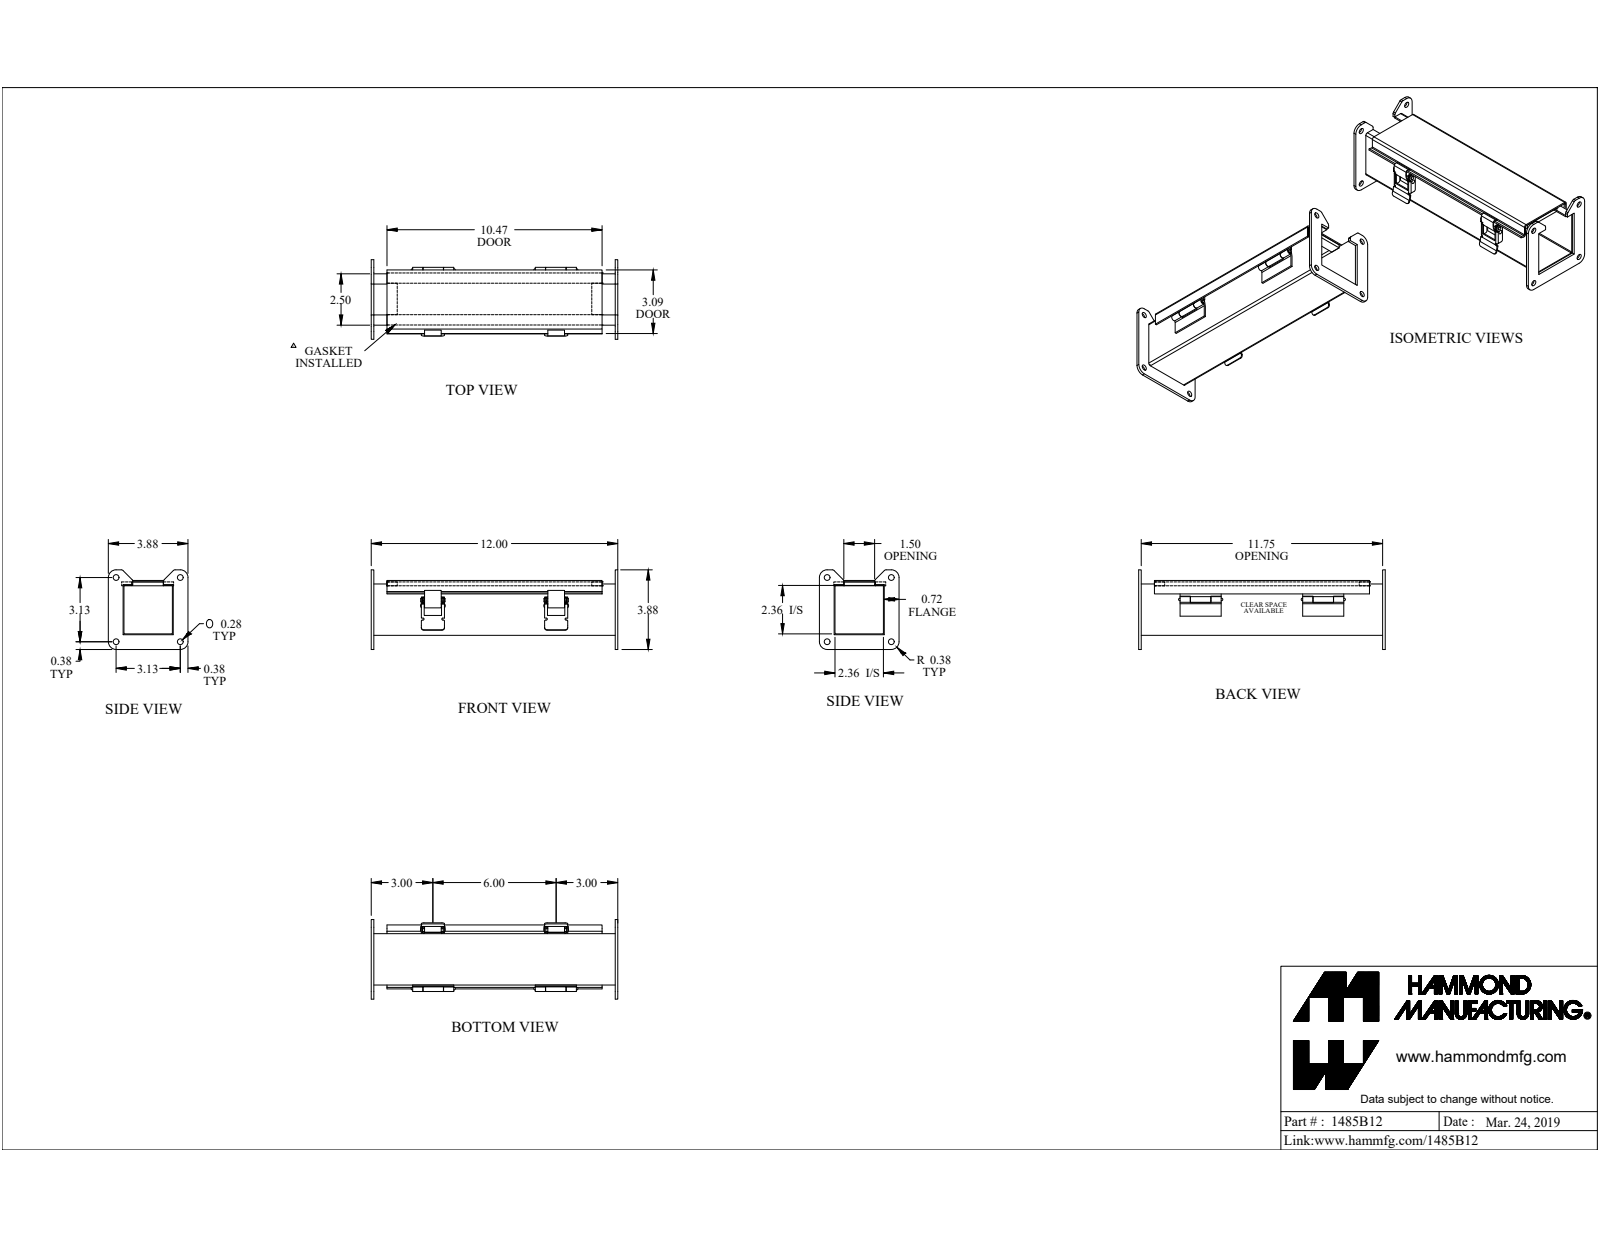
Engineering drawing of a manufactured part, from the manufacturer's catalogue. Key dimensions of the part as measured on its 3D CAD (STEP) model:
Part name (STEP PRODUCT): 1485B12
STEP written by: SolidWorks 2019 (CONFIG_CONTROL_DESIGN)
Units: inches
Bodies: 20 solids, 380 faces (230 planar, 138 cylindrical, 12 other)
Overall size (bounding box): 12 × 3.875 × 3.875
Volume: 15.15 in³ · Surface area: 390.3 in²
Round holes (diameter × count): ⌀0.281 ×4, ⌀0.125 ×1, ⌀0.164 ×1
Round bosses / shafts (diameter × count): ⌀0.275 ×1, ⌀0.162 ×1, ⌀0.158 ×1, ⌀0.125 ×1, ⌀0.125 ×1
Partial cylindrical surfaces — rounded edges, fillets, slot ends (radius × count): R0.125 ×9, R0.029 ×8, R0.086 ×8, R0.036 ×7, R0.108 ×7, R0.015 ×4, R0.047 ×4, R0.375 ×4
Main face-to-face distances: 0.072, 2.428, 2.6, 2.5, 2.356, 2.672, 2.528, 0.172, 0.028, 0.044
Hole centre spacings: 3.125, 4.42, 1.075, 1.1, 2.028, 2.063, 2.927, 3.174
